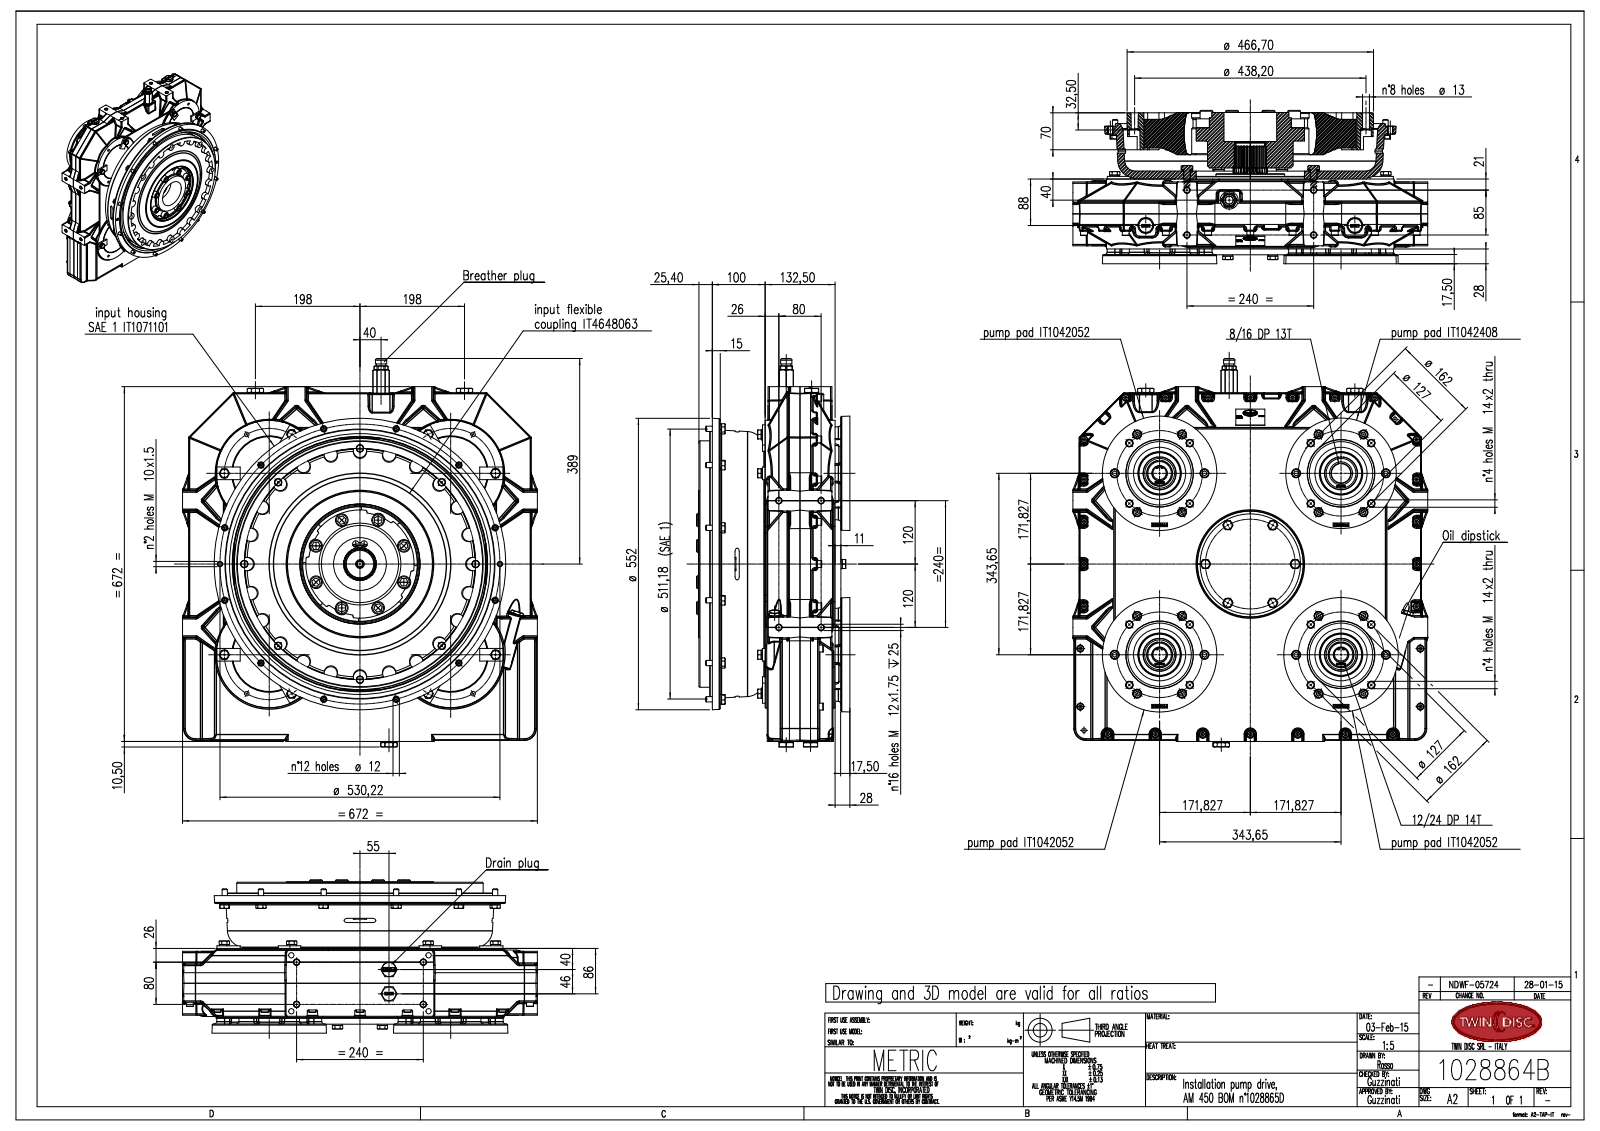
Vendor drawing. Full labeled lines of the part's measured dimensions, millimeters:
Part name (STEP PRODUCT): IT1071101_rev01-installation; 1028864B; ITB00710000_rev01-installation; ITam230-001_rev01-installation (+8 more)
STEP written by: SolidWorks 2007 (AUTOMOTIVE_DESIGN)
Units: millimetres
Bodies: 121 solids, 11635 faces (4294 planar, 3900 cylindrical, 3441 other)
Overall size (bounding box): 735.8 × 672 × 290.5
Volume: 19 910 000 mm³ · Surface area: 5 911 000 mm²
Round holes (diameter × count): ⌀8.5 ×70, ⌀10.2 ×43, ⌀12 ×42, ⌀17 ×32, ⌀11 ×30, ⌀14 ×29, ⌀13 ×15, ⌀10 ×12, ⌀16 ×7, ⌀2 ×6, ⌀12.2 ×6, ⌀80 ×5
Round bosses / shafts (diameter × count): ⌀10 ×44, ⌀16 ×34, ⌀13 ×28, ⌀8 ×28, ⌀16.2 ×27, ⌀18.1 ×26, ⌀24 ×8, ⌀19 ×8
Partial cylindrical surfaces — rounded edges, fillets, slot ends (radius × count): R2.5 ×370, R2 ×130, R12.5 ×72, R0.45 ×58, R4.5 ×36, R1.5 ×27, R5 ×24, R3 ×20
Main face-to-face distances: 66, 128.5, 4, 143.5, 15, 62, 62.5, 28, 66.5, 32
Hole centre spacings: 202.52, 266.83, 304.21, 90, 127.28, 35.12, 100, 140.24
